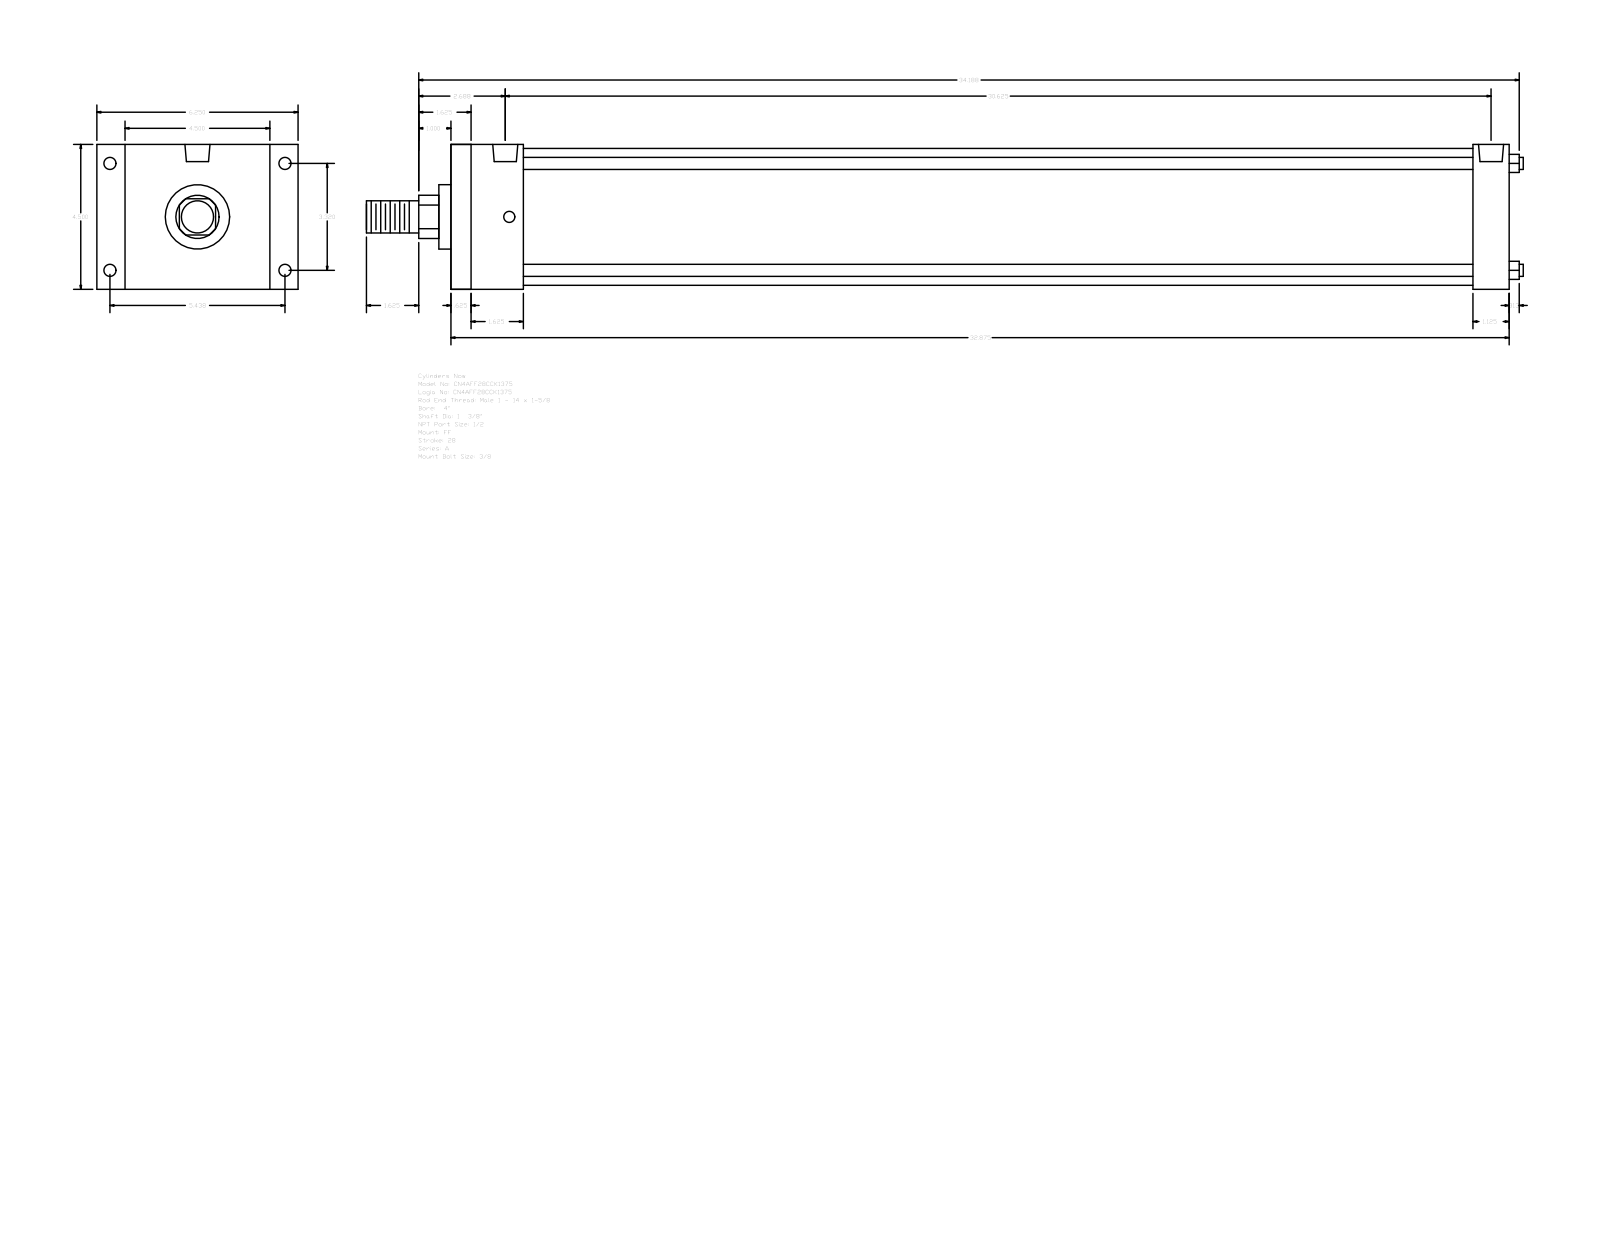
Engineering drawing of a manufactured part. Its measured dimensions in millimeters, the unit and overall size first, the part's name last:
Units: millimetres
Overall size (bounding box): 912.81 × 158.75 × 114.3
Round holes (diameter × count): ⌀8.73 ×4, ⌀9.53 ×4, ⌀19.77 ×2
Round bosses / shafts (diameter × count): ⌀9.53 ×4, ⌀107.95 ×1, ⌀50.8 ×1, ⌀34.92 ×1, ⌀25.4 ×1
Partial cylindrical surfaces — rounded edges, fillets, slot ends (radius × count): R17.06 ×1
Main face-to-face distances: 114.3, 835.02, 819.15, 15.87, 57.15, 28.57, 22.23, 136.53, 806.45, 790.58
Hole centre spacings: 3.18, 84.32, 138.12, 161.82, 771.52, 774.7, 777.88
Bodies: 0 solids, 92 faces (64 planar, 28 cylindrical, 0 other)
Part name (STEP PRODUCT): A_FF__0400_1.375
STEP written by: GSSL Pune (CONFIG_CONTROL_DESIGN)
